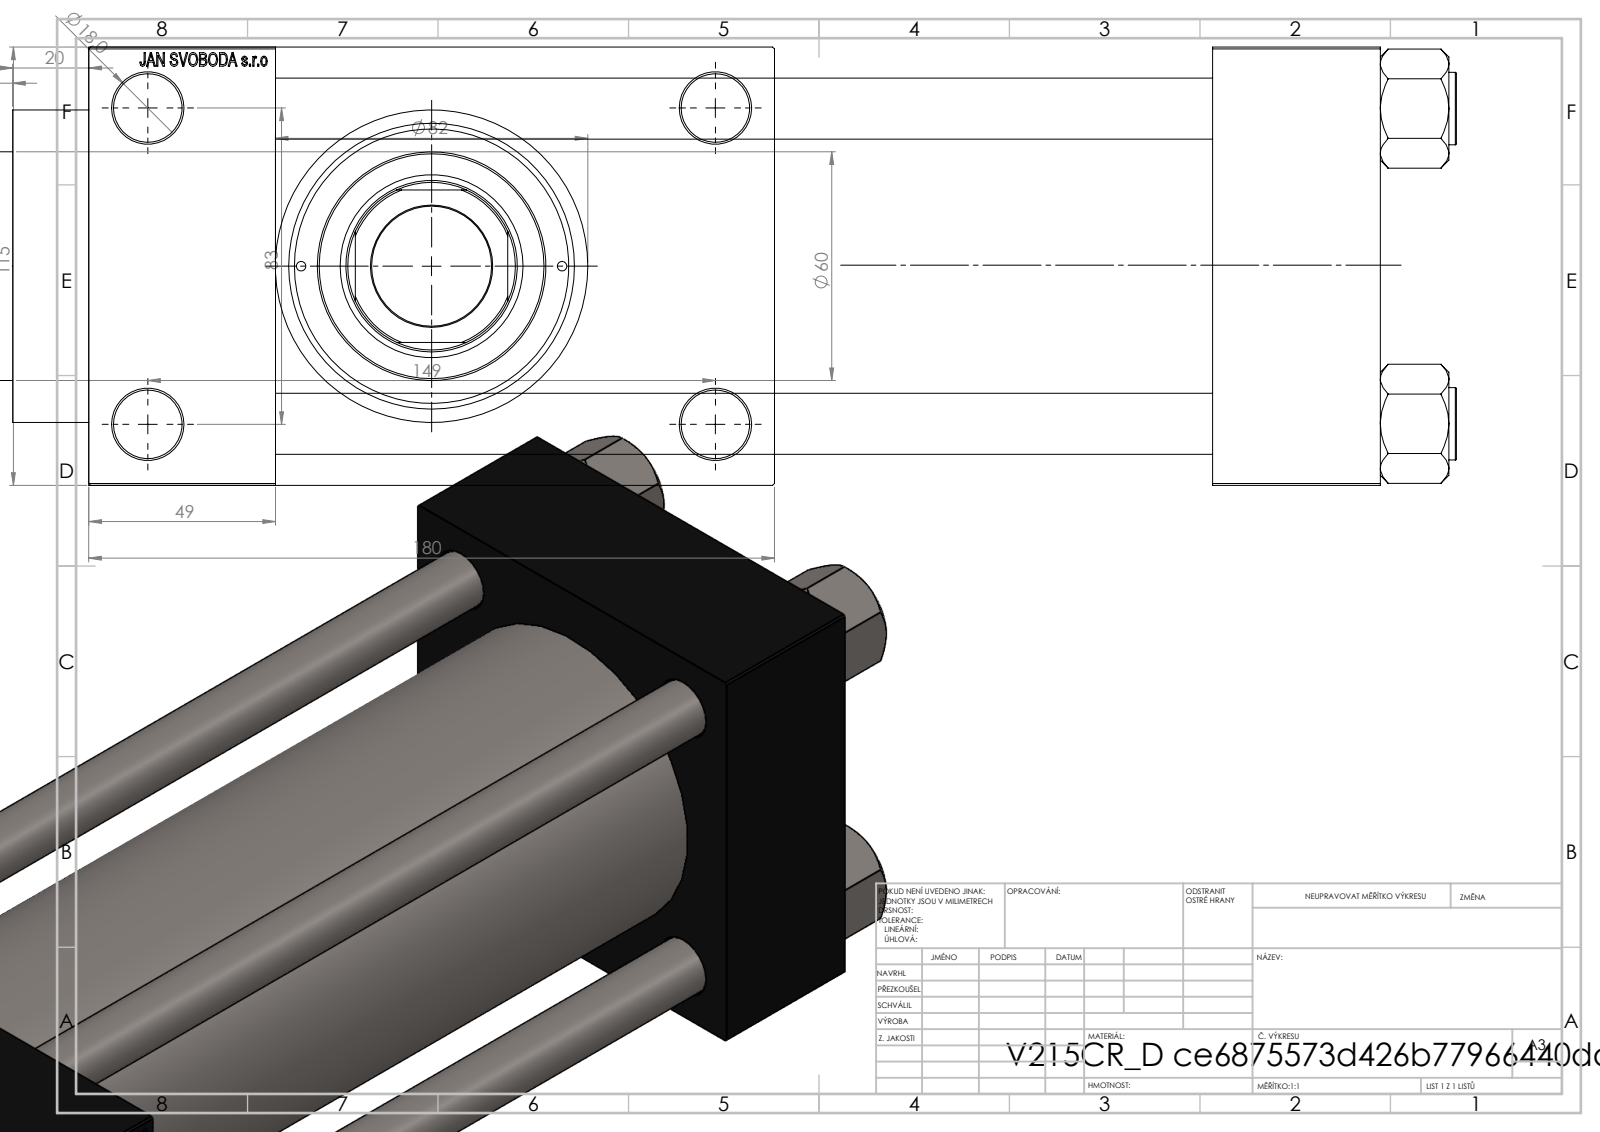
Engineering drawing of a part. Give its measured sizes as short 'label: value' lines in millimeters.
name: V215CR_D_Body; V215CR_VCP_D; V215CR_D_TYCINKA; V215_VC_A (+1 more)
written by: SolidWorks 2019 (CONFIG_CONTROL_DESIGN)
unit: mm
bodies: 11 solids, 1159 faces (547 planar, 92 cylindrical, 520 other)
size: 410 × 180 × 115
volume: 2 576 000 mm³; area: 457 840 mm²
holes: 4× ⌀16, 4× ⌀18, 2× ⌀2.5, 2× ⌀7, 2× ⌀26.44, 2× ⌀35, 1× ⌀31.5, 1× ⌀45, 1× ⌀48, 1× ⌀61, 1× ⌀72, 1× ⌀80
bosses: 4× ⌀19, 1× ⌀86, 1× ⌀82, 1× ⌀60
rounds: 1× R22
face distances: 115, 246, 295, 49, 44, 290, 339, 32.5, 147.5, 180
hole spacings: 33.15, 41.96, 57.81, 58.48, 82.7, 85.28, 86.17, 89.24
